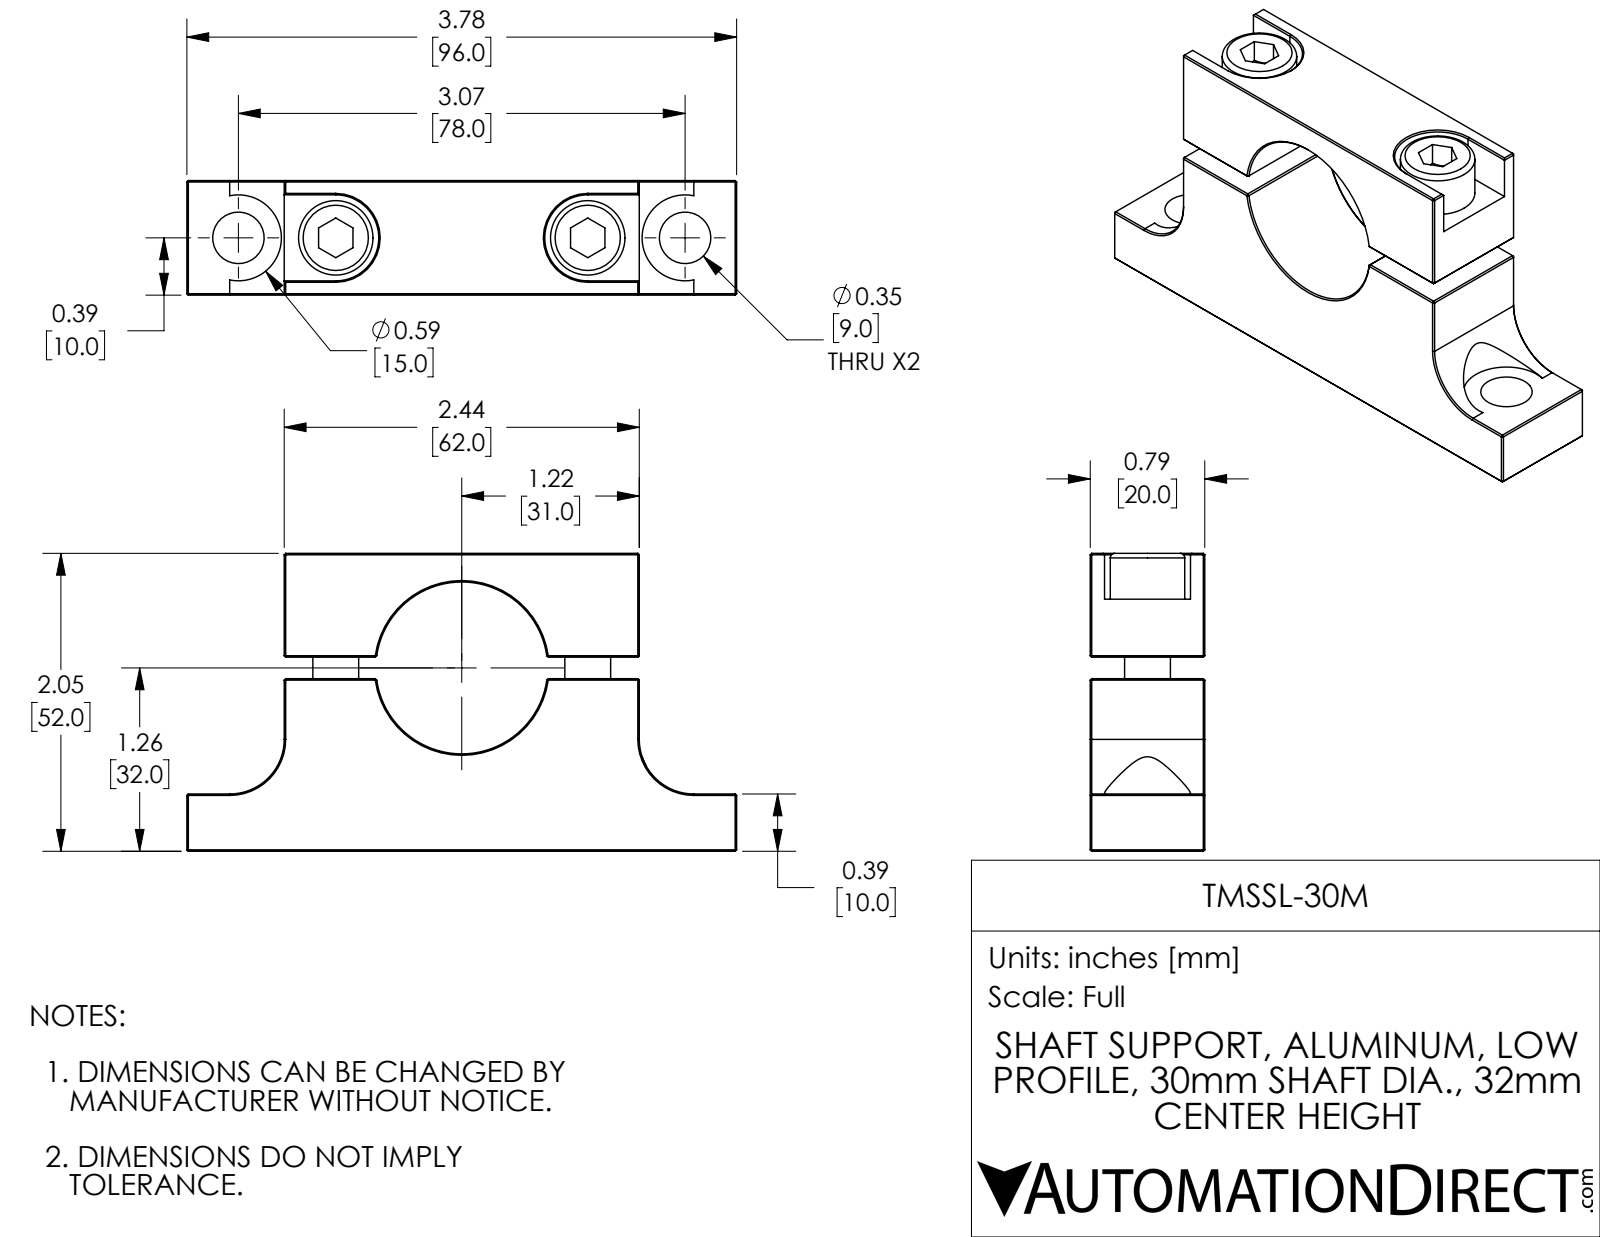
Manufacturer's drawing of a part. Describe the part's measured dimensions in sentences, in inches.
The part is named "TMSSL-30M". Its 3-D file was written by "SolidWorks 2017 (AUTOMOTIVE_DESIGN)". It is 4 solids with 178 faces: 118 planar, 32 cylindrical and 28 other. Overall it measures 3.78 by 2.047 by 0.787 inches. Its volume is 3.217 cubic inches and its surface area 29.22 square inches. Round holes: 4 of diameter 0.354, 2 of diameter 0.194, 1 of diameter 0.094, 1 of diameter 1.181. Round bosses or shafts: 2 of diameter 0.512, 2 of diameter 0.315. Partial cylindrical surfaces (rounded edges, fillets, slot ends): 4 of radius 0.296, 2 of radius 0.375. The main face-to-face distances are 0.787, 2.047, 1.732, 1.333, 0.714, 0.399, 0.315, 2.441, 0.394, 0.94. The hole center spacings are 0.669, 0.866, 1.535, 2.402, 1.732, 3.071.
